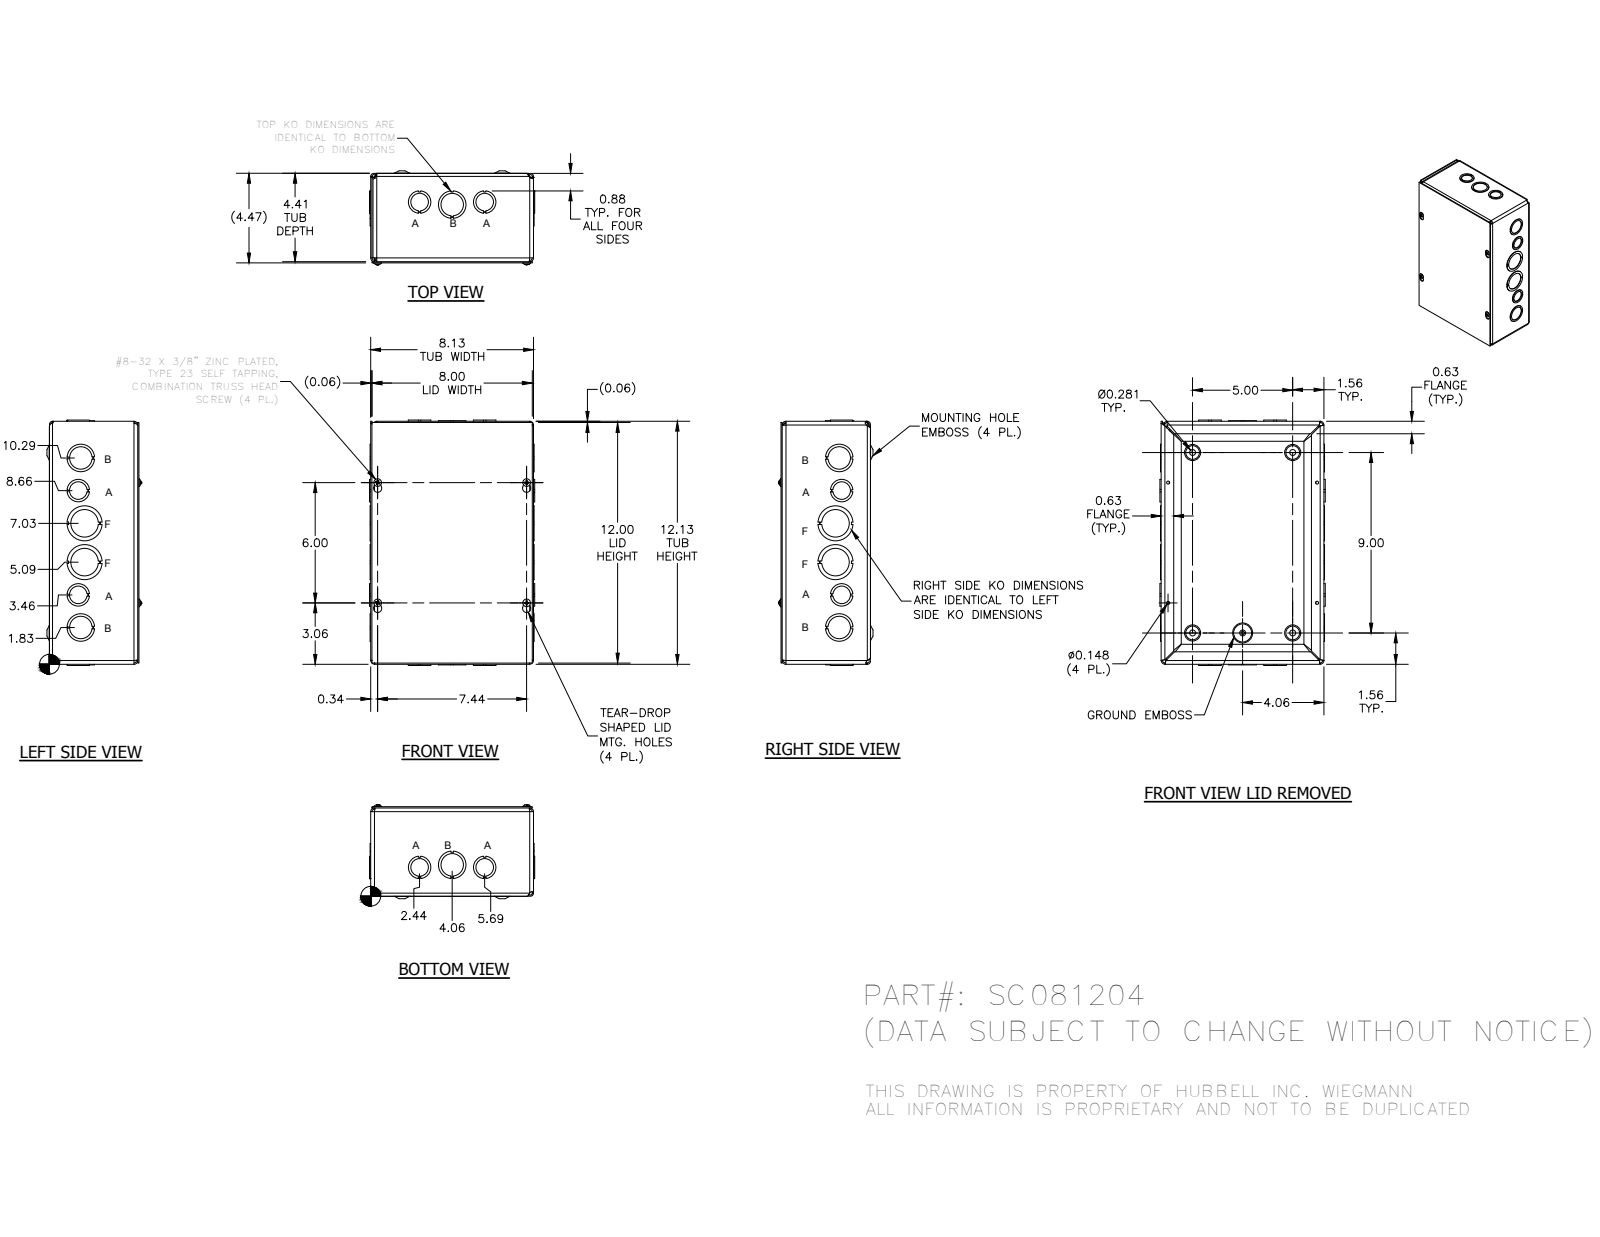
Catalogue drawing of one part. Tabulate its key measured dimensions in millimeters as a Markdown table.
| quantity | value |
| --- | --- |
| part name | SC0812BKP; SC081204WRA; SC0812LID; 34056 (+1 more) |
| STEP written by | Autodesk Inventor 2014 (AUTOMOTIVE_DESIGN) |
| units | millimeters |
| bodies | 22 solids, 862 faces (529 planar, 175 cylindrical, 158 other) |
| overall size | 311.12 × 209.53 × 119.2 |
| round holes (diameter × count) | 28.57 × 7, 34.92 × 5, 3.76 × 4, 7.62 × 4, 22.22 × 4, 44.45 × 2, 4.19 × 1 |
| round bosses / shafts (diameter × count) | 9.75 × 4, 4.17 × 4, 5.8 × 1 |
| partial cylindrical surfaces (radius × count) | 3.17 × 12, 4.75 × 8, 1.4 × 4, 1.57 × 4, 2.38 × 4, 2.97 × 4, 3.15 × 4, 3.96 × 4 |
| main face-to-face distances | 1.57, 110.32, 1.58, 111.89, 1.59, 111.91, 113.48, 206.38, 204.8, 204.81 |
| hole center spacings | 49.09, 193, 41.52, 42.15, 63.5, 82.94, 91.03, 101.85 |
